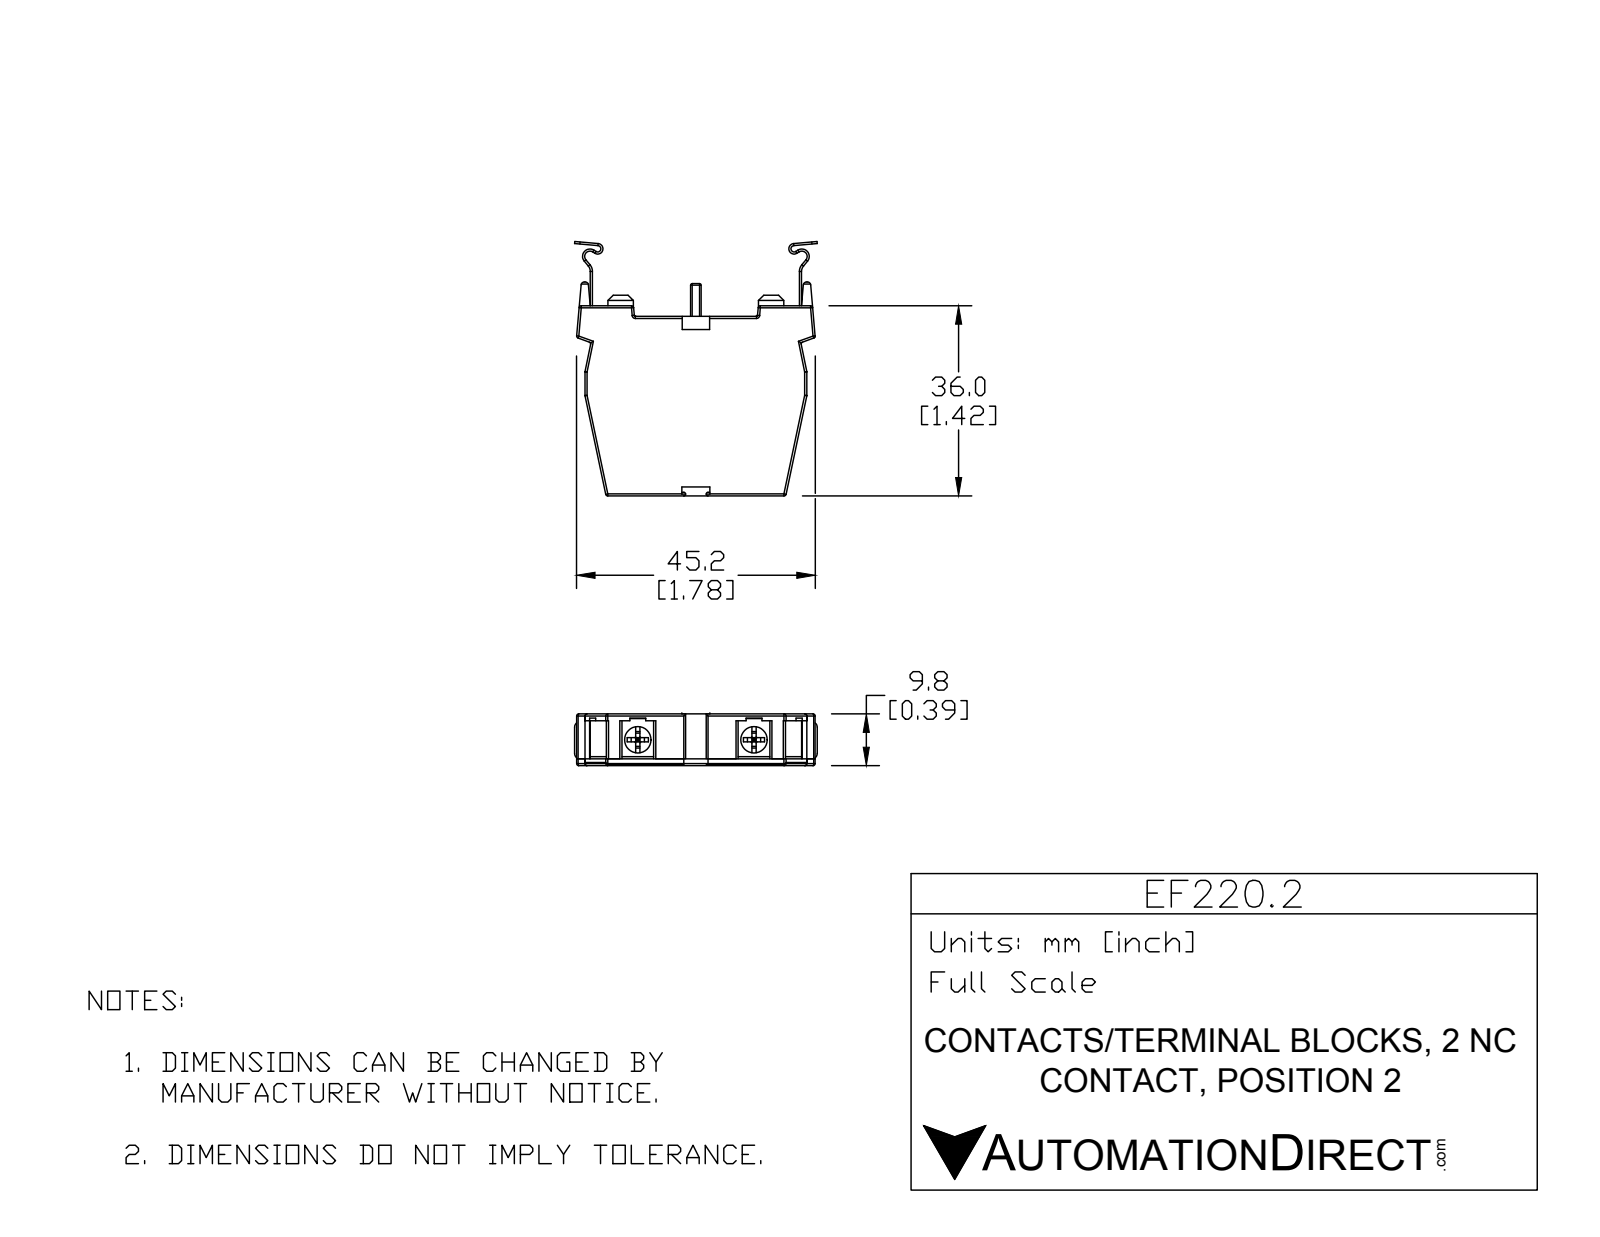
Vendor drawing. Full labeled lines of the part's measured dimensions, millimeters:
Part name (STEP PRODUCT): EF220.2
STEP written by: SolidWorks 2015 (AUTOMOTIVE_DESIGN)
Units: millimetres
Bodies: 7 solids, 299 faces (173 planar, 104 cylindrical, 22 other)
Overall size (bounding box): 48.16 × 46.28 × 9.8
Volume: 12 135 mm³ · Surface area: 6 604 mm²
Round holes (diameter × count): ⌀5 ×4
Round bosses / shafts (diameter × count): ⌀4 ×4, ⌀4.75 ×2
Partial cylindrical surfaces — rounded edges, fillets, slot ends (radius × count): R0.25 ×44, R0.5 ×8, R1 ×6, R0.6 ×4, R0.6 ×2, R1 ×2, R1.4 ×2, R1.6 ×2
Main face-to-face distances: 9.8, 1.4, 8.4, 34, 7, 2, 0.4, 3.18, 37.18, 36
Hole centre spacings: 21.81
